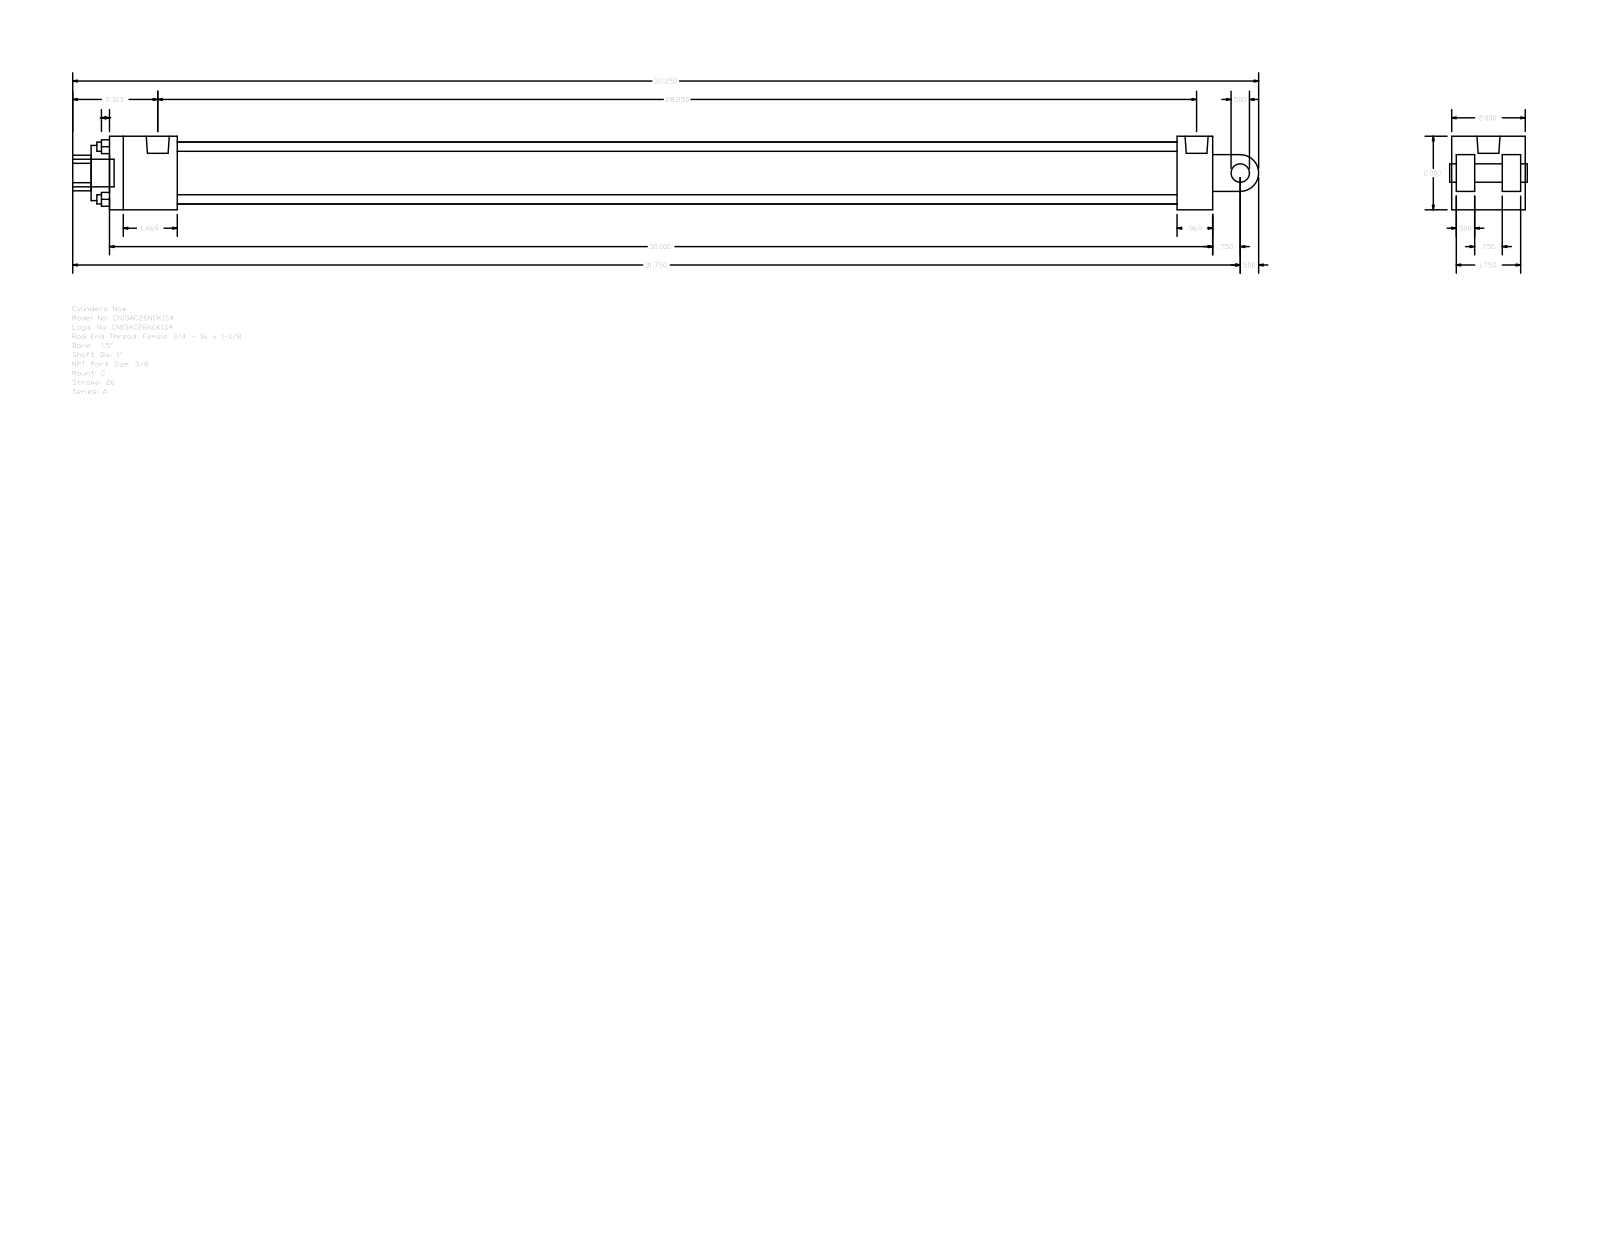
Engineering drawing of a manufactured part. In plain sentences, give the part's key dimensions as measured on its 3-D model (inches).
The part is named "A_C__0150_1". Its 3-D file was written by "GSSL Pune (CONFIG_CONTROL_DESIGN)". It is 0 solids with 99 faces: 70 planar, 29 cylindrical and 0 other. Overall it measures 32.25 by 2 by 2 inches. Round holes: 4 of diameter 0.25, 2 of diameter 0.219, 1 of diameter 0.627, 1 of diameter 1, 1 of diameter 1.5, 1 of diameter 1.69. Round bosses or shafts: 2 of diameter 0.219, 1 of diameter 0.75, 1 of diameter 0.627, 1 of diameter 0.5. Partial cylindrical surfaces (rounded edges, fillets, slot ends): 1 of radius 0.484, 1 of radius 0.5. The main face-to-face distances are 2, 0.5, 0.125, 0.625, 1.875, 1.375, 1.25, 30, 29.031, 0.969. The hole center spacings are 1.011, 1.43, 2.022, 0.156.
